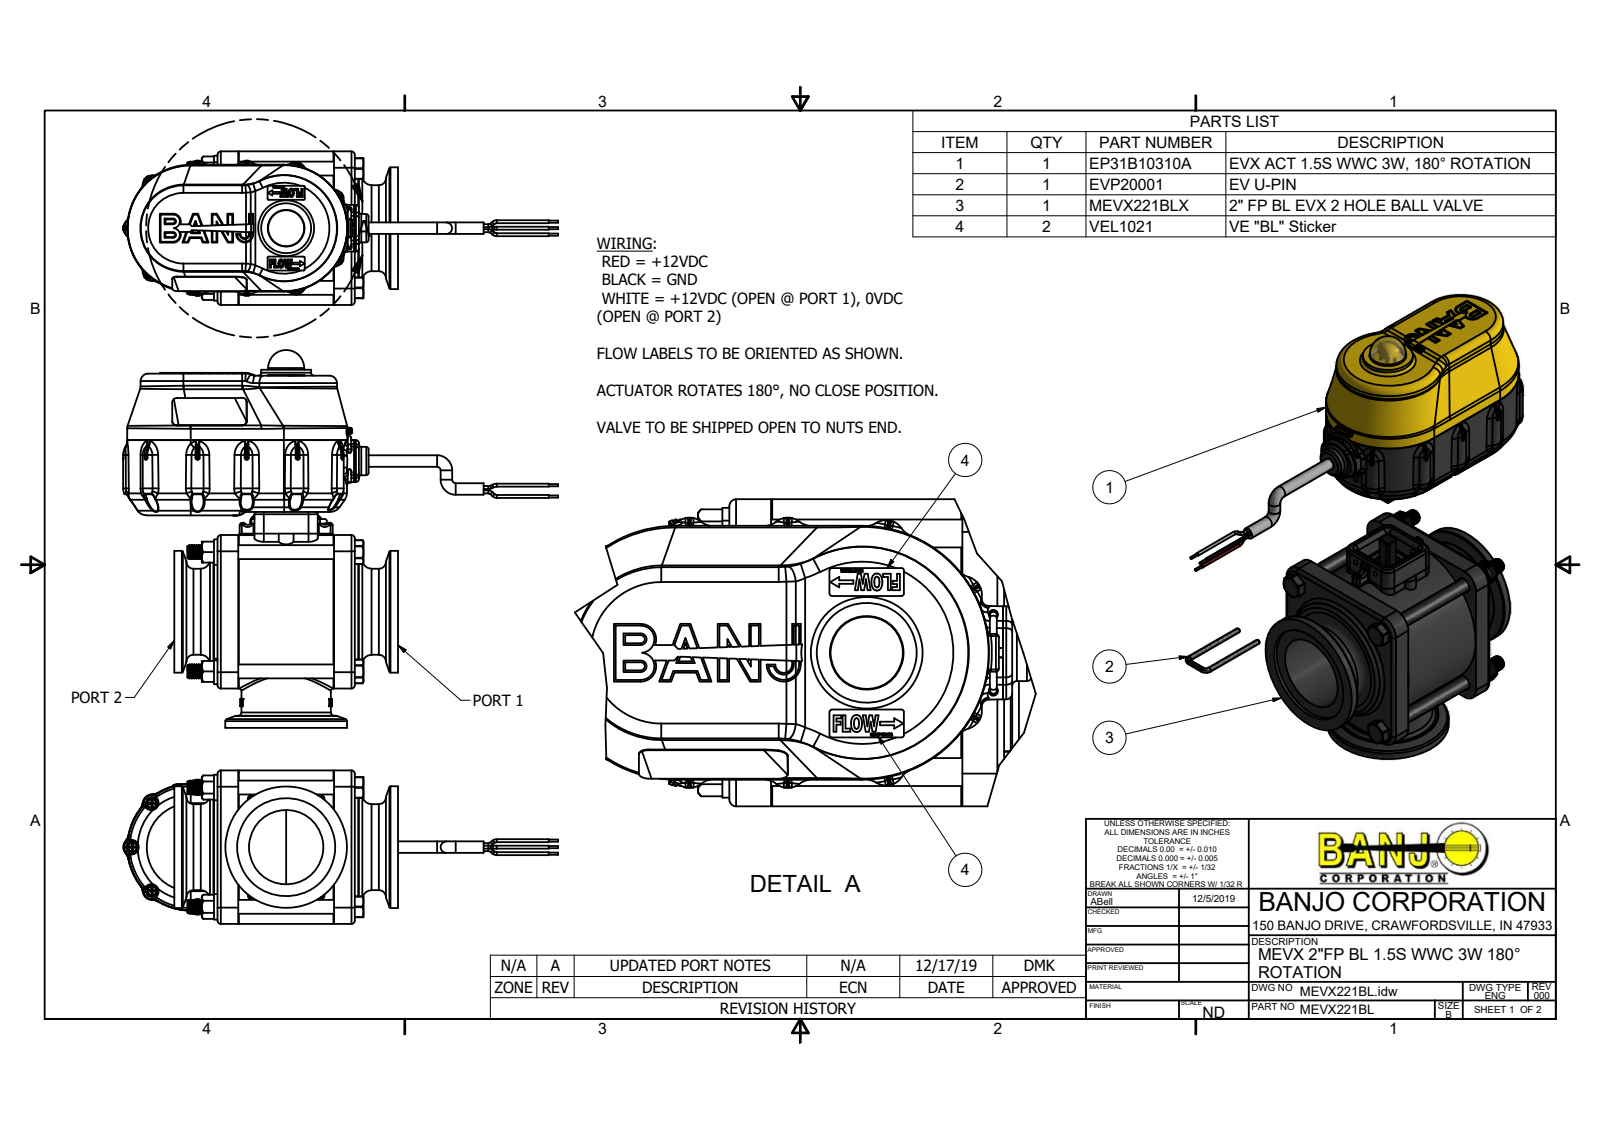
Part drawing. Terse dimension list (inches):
name: MEVX221BL; MEVX221BLX; MEVX25354AB; MEVX25354ABX (+8 more)
written by: Autodesk Inventor 2019 (AUTOMOTIVE_DESIGN)
unit: in
bodies: 94 solids, 11461 faces (3192 planar, 3201 cylindrical, 5068 other)
size: 11.685 × 10.15 × 4.125
volume: 101 in³; area: 798.8 in²
holes: 11× ⌀0.095, 11× ⌀0.15, 7× ⌀0.08, 4× ⌀0.107, 4× ⌀0.126, 4× ⌀0.136, 4× ⌀0.148, 4× ⌀0.15, 4× ⌀0.17, 4× ⌀0.307, 4× ⌀0.385, 4× ⌀0.438
bosses: 60× ⌀0.324, 17× ⌀0.25, 15× ⌀0.08, 11× ⌀0.14, 11× ⌀0.108, 11× ⌀0.085, 6× ⌀0.058, 5× ⌀0.375
rounds: 180× R0.013, 145× R0.04, 88× R0.01, 74× R0.02, 49× R0.005, 49× R0.03, 34× R0.015, 28× R0.08
face distances: 0.1, 2.565, 0.06, 0.729, 0.645, 3.045, 2.485, 0.56, 3.13, 0.085
hole spacings: 2.265, 2.715, 3.204, 1.662, 1.774, 2.458, 2.69, 2.73
